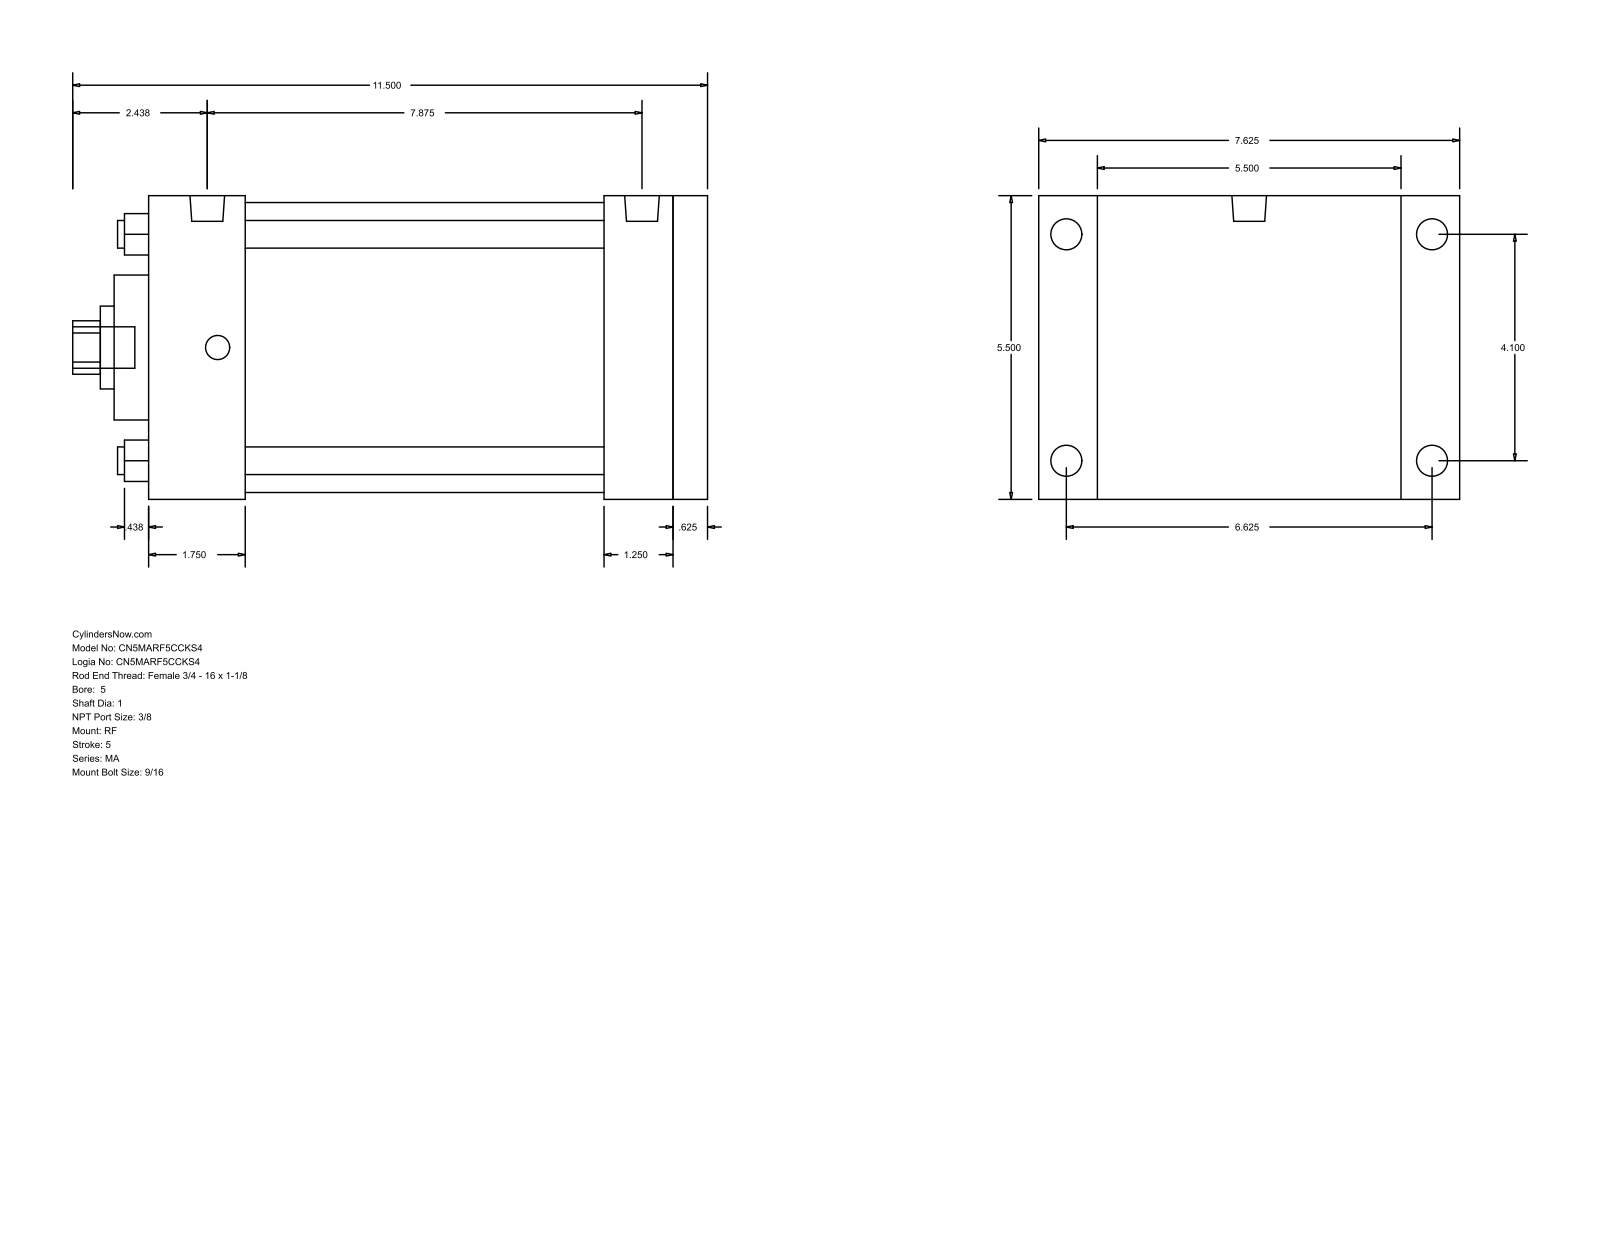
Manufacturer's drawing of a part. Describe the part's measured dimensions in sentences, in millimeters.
The part is named "MA_RF__0500_1". Its 3-D file was written by "GSSL Pune (CONFIG_CONTROL_DESIGN)". It is 0 solids with 94 faces: 65 planar, 29 cylindrical and 0 other. Overall it measures 292.1 by 193.68 by 139.7 millimeters. Round holes: 4 of diameter 12.7, 1 of diameter 25.4, 1 of diameter 38.1, 1 of diameter 66.67, 1 of diameter 133.35. Round bosses or shafts: 4 of diameter 14.29, 4 of diameter 11.11, 2 of diameter 15.93, 1 of diameter 19.05. Partial cylindrical surfaces (rounded edges, fillets, slot ends): 1 of radius 12.29. The main face-to-face distances are 139.7, 257.18, 15.87, 241.31, 165.09, 44.46, 196.85, 212.72, 209.55, 31.76. The hole center spacings are 73.64, 104.14, 147.28.
